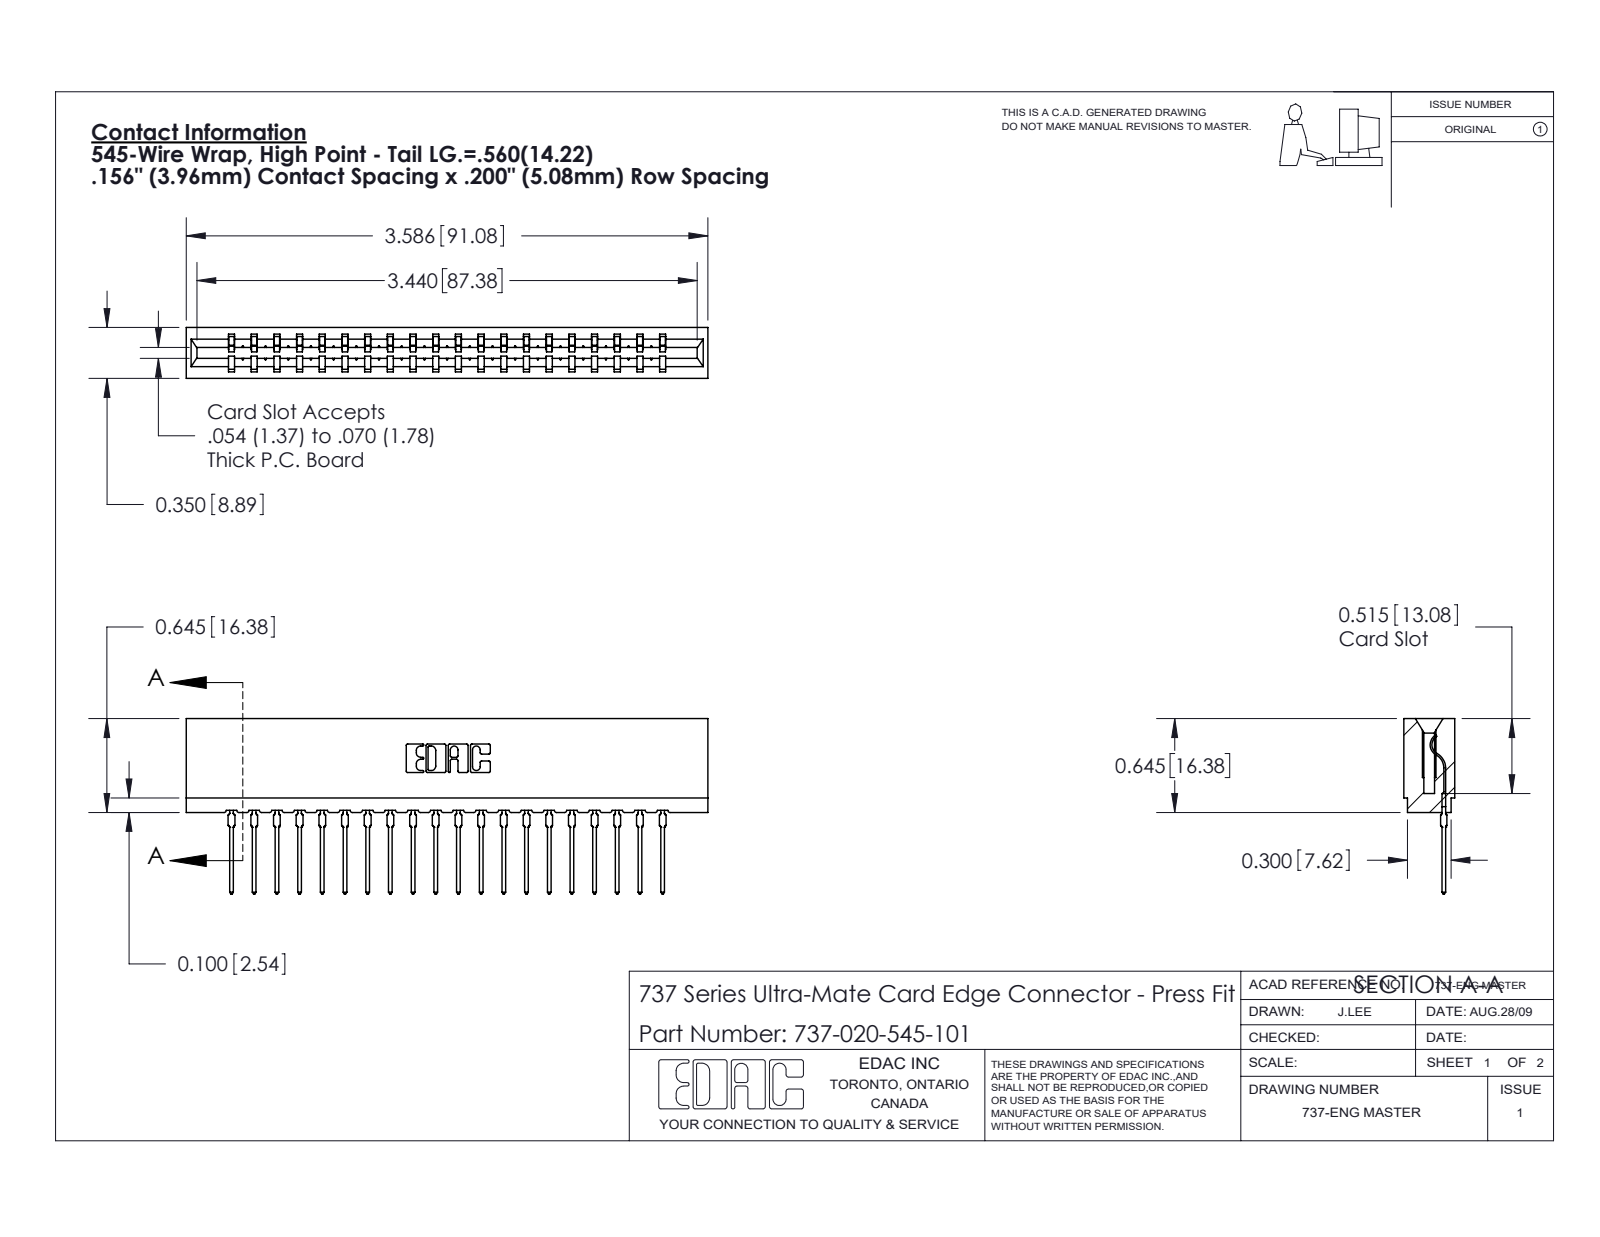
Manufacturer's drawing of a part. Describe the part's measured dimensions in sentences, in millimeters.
The part is named "737-020-545-101; 737 Part_Insulator Option - 01; 745-292-001_545". Its 3-D file was written by "SolidWorks 2020 (CONFIG_CONTROL_DESIGN)". It is 21 solids with 2354 faces: 1414 planar, 420 cylindrical and 520 other. Overall it measures 91.1 by 30.6 by 8.9 millimeters. Its volume is 9 010 cubic millimeters and its surface area 12 030 square millimeters. Partial cylindrical surfaces (rounded edges, fillets, slot ends): 40 of radius 0.4, 40 of radius 0.5, 22 of radius 0.3, 6 of radius 0.2, 6 of radius 0.8, 4 of radius 0.1, 4 of radius 0.3, 3 of radius 0.7. The main face-to-face distances are 3.5, 5.4, 8.9, 4, 19.8, 15.8, 1.9, 1.1, 7.7, 2.4.
